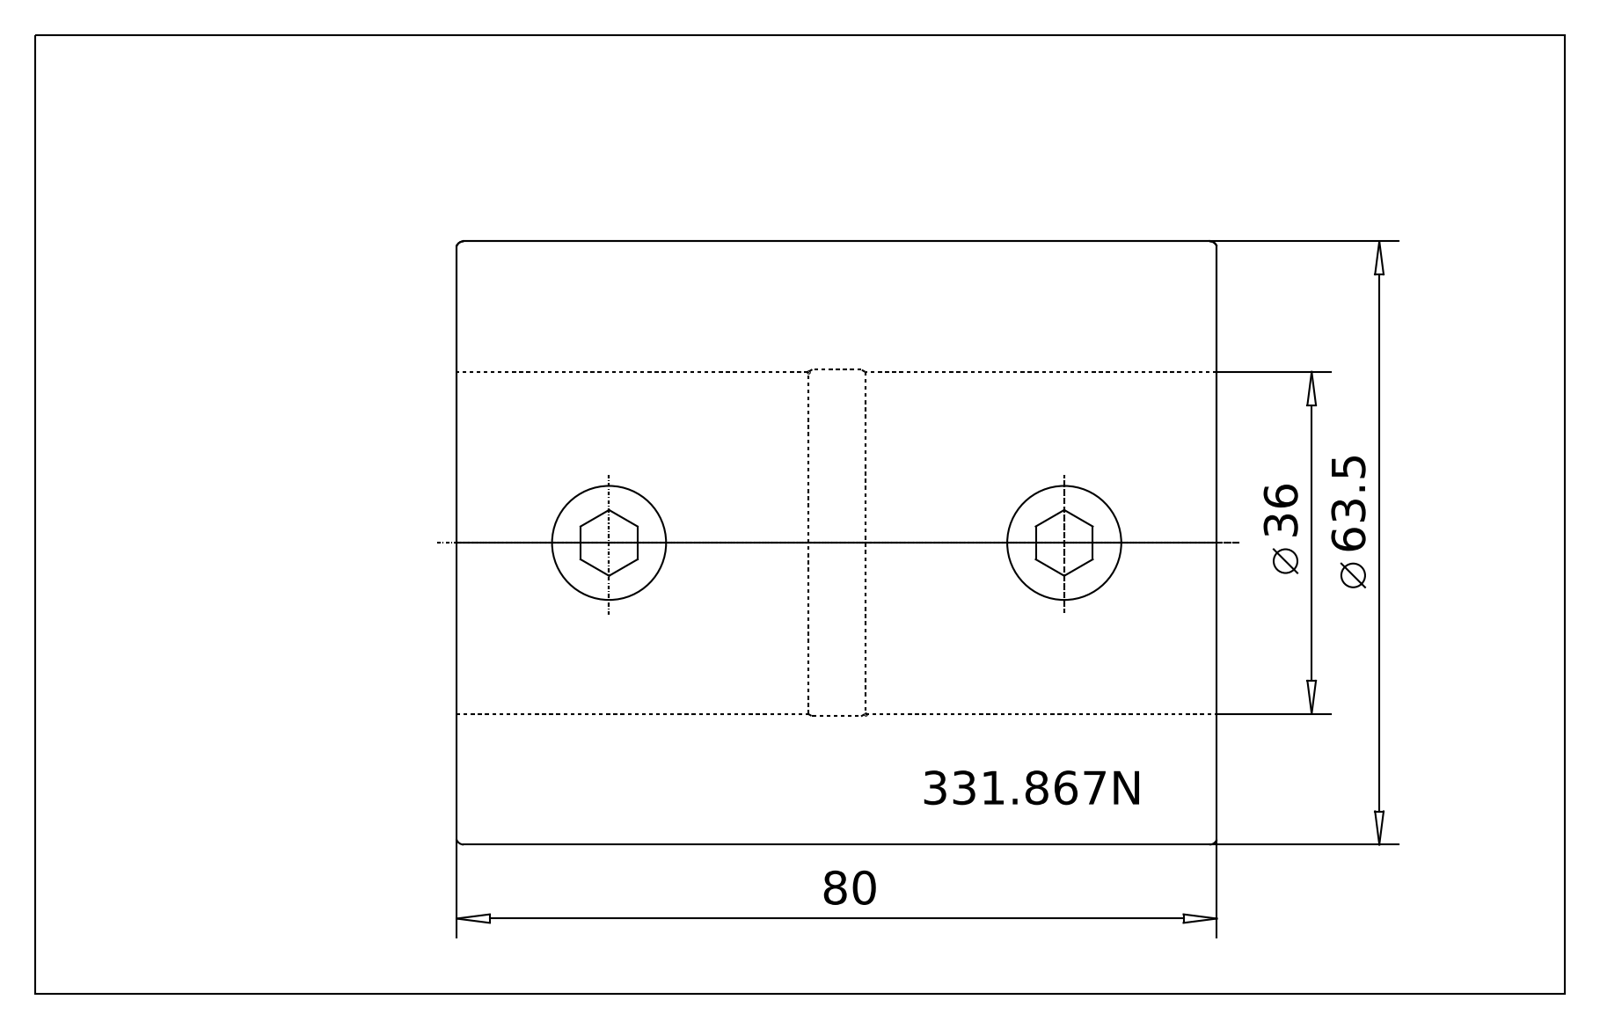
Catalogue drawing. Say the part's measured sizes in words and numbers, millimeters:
The part is named "331.867N Kaiser R CKN6 X CKN6 X 100 AL|331.867N Kaiser R CKN6 X CKN6 X 100 AL;NONE; 331.867N Kaiser R CKN6 X CKN6 X 100 AL|690.436 Kaiser ETL M12 X 18 CK6;NONE". Its 3-D file was written by "ACIS (automotive_design)". It is 7 solids with 241 faces: 89 planar, 74 cylindrical and 78 other. Overall it measures 80 by 63.5 by 63.5 millimeters. Its volume is 171 858 cubic millimeters and its surface area 36 814 square millimeters. Round holes: 6 of diameter 11.04, 6 of diameter 12.55, 6 of diameter 13.4, 3 of diameter 5, 1 of diameter 4.2, 1 of diameter 6, 1 of diameter 7.55, 1 of diameter 36, 1 of diameter 36.5. Round bosses or shafts: 6 of diameter 12, 1 of diameter 63.5. Partial cylindrical surfaces (rounded edges, fillets, slot ends): 1 of radius 31.75. The main face-to-face distances are 80, 6, 18, 23.95, 13.05, 66.95, 19.05, 60.95, 47.9, 5.99. The hole center spacings are 47.9, 11.15, 23.95, 35.1, 59.05, 25, 70.2.
